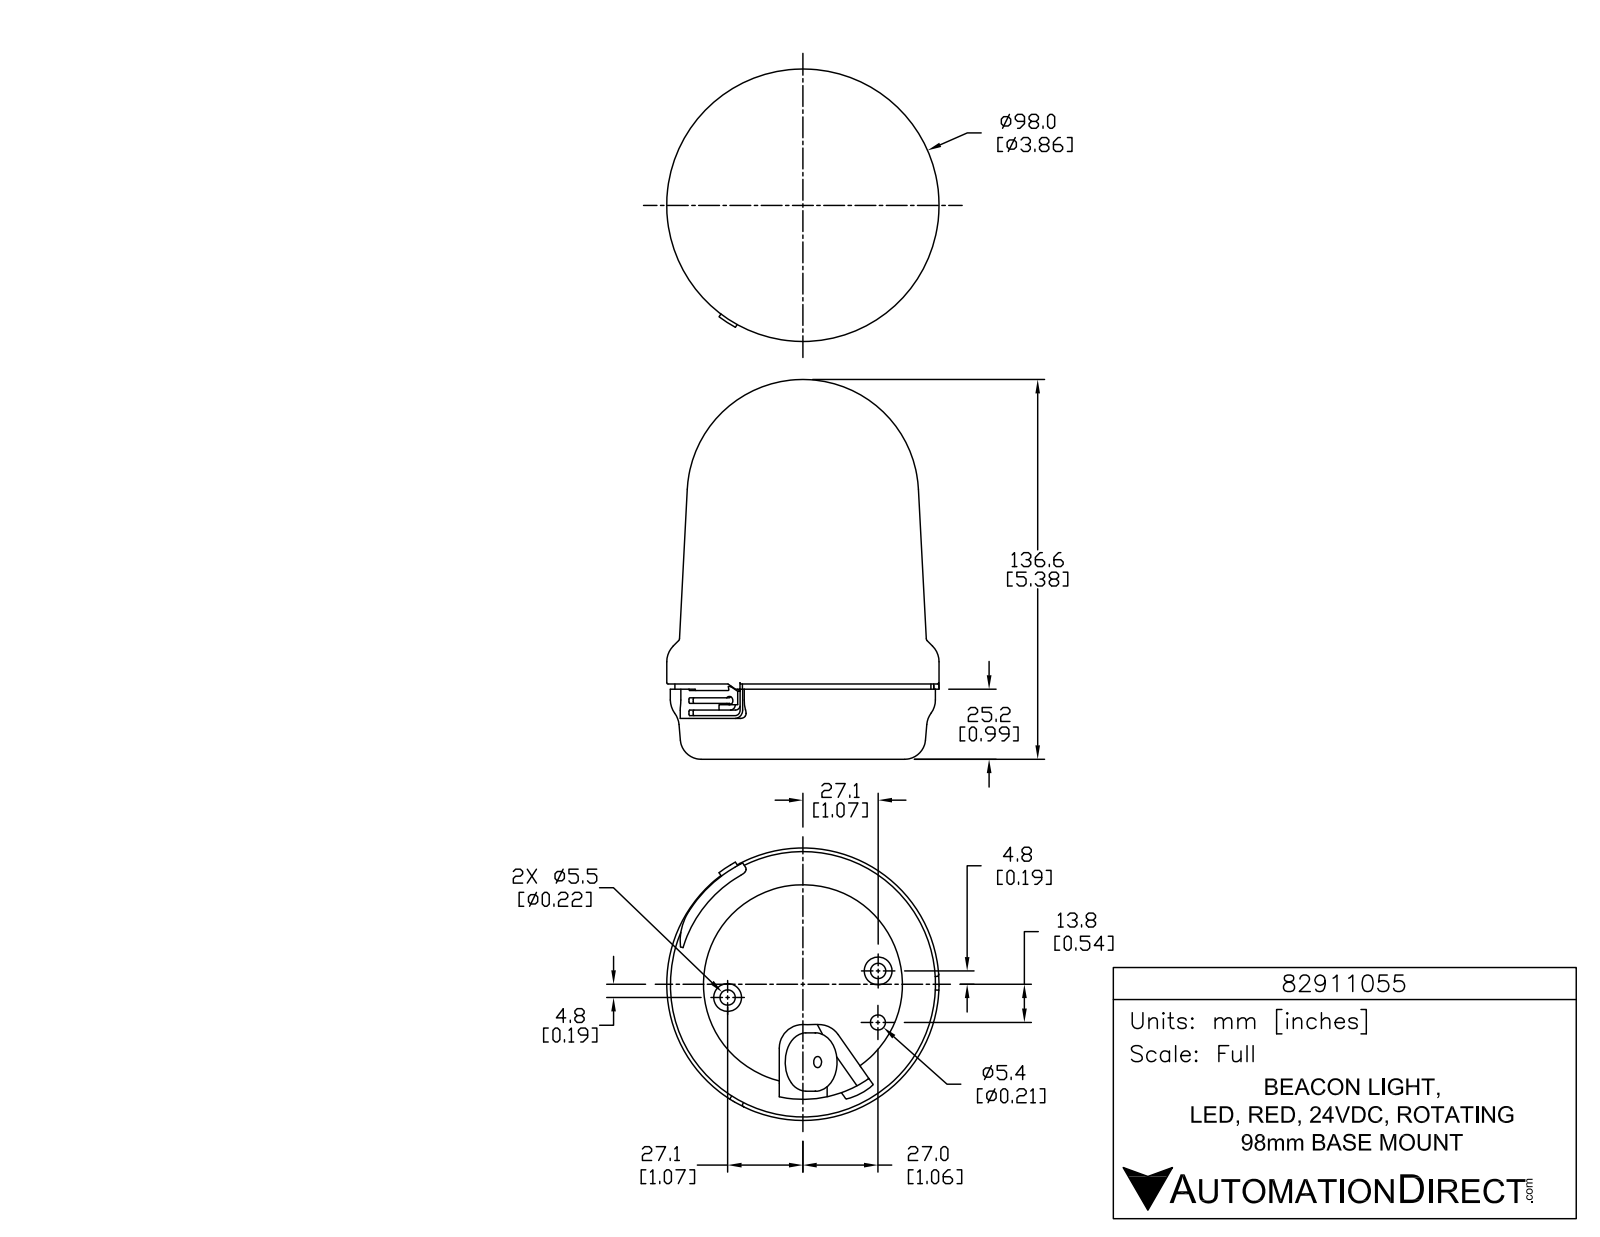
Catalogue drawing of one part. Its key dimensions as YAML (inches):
part_name: "82911055"
step_written_by: "SolidWorks 2015 (AUTOMOTIVE_DESIGN)"
units: inches
bodies: {solids: 1, faces: 872, planar: 566, cylindrical: 204, other: 102}
overall_size: [5.378, 3.858, 3.858]
volume: 44.69
surface_area: 73.66
round_holes:
  - {diameter: 0.059, count: 3}
  - {diameter: 0.217, count: 2}
  - {diameter: 0.157, count: 1}
  - {diameter: 0.213, count: 1}
  - {diameter: 2.819, count: 1}
round_bosses_or_shafts:
  - {diameter: 0.339, count: 3}
  - {diameter: 0.084, count: 3}
  - {diameter: 0.394, count: 2}
  - {diameter: 3.858, count: 1}
  - {diameter: 3.756, count: 1}
  - {diameter: 3.626, count: 1}
  - {diameter: 0.827, count: 1}
partial_cylinders:
  - {radius: 0.005, count: 9}
  - {radius: 0.005, count: 6}
  - {radius: 0.012, count: 6}
  - {radius: 0.012, count: 6}
  - {radius: 0.012, count: 6}
  - {radius: 0.196, count: 6}
  - {radius: 0.02, count: 5}
  - {radius: 0.039, count: 4}
face_to_face_distances: [1.045, 0.972, 0.073, 0.02, 0.992, 1.065, 0.236, 0.579, 0.559, 0.413]
hole_center_spacings: [1.083, 0.73, 1.193, 2.158, 2.165]
